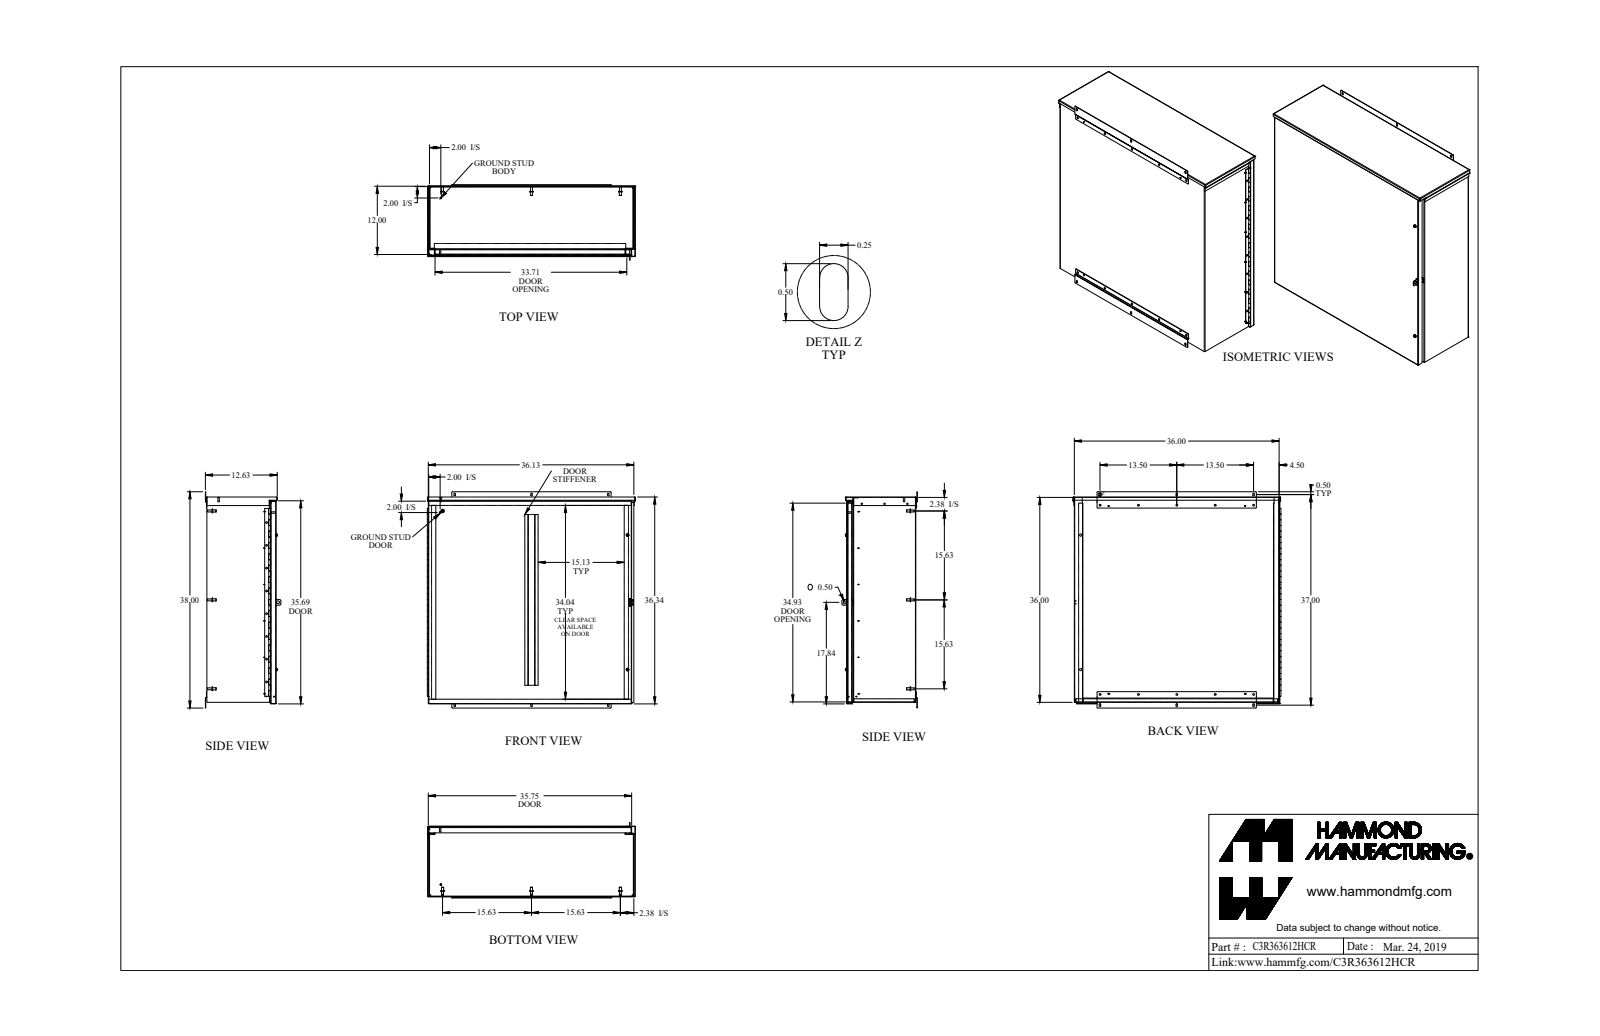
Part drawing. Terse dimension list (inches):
name: C3R363612HCR_Default
written by: SolidWorks 2019 (CONFIG_CONTROL_DESIGN)
unit: in
bodies: 39 solids, 1166 faces (609 planar, 471 cylindrical, 86 other)
size: 38 × 36.571 × 13.26
volume: 394.5 in³; area: 10 754 in²
holes: 10× ⌀0.312, 8× ⌀0.304, 4× ⌀0.137, 4× ⌀0.14, 3× ⌀0.25, 3× ⌀0.26, 3× ⌀0.313, 2× ⌀0.266, 2× ⌀0.28, 2× ⌀0.29, 2× ⌀0.397, 1× ⌀0.188
bosses: 12× ⌀0.131, 8× ⌀0.65, 8× ⌀0.375, 8× ⌀0.33, 3× ⌀0.51, 3× ⌀0.244, 3× ⌀0.187, 2× ⌀0.5
rounds: 39× R0.036, 39× R0.108, 23× R0.125, 3× R0.171, 2× R0.25
face distances: 0.072, 12.1, 12.172, 12.028, 36, 35.928, 36.072, 35.856, 0.259, 0.187
hole spacings: 4, 6.75, 8, 33.929, 13.5, 12, 35.887, 1.505
